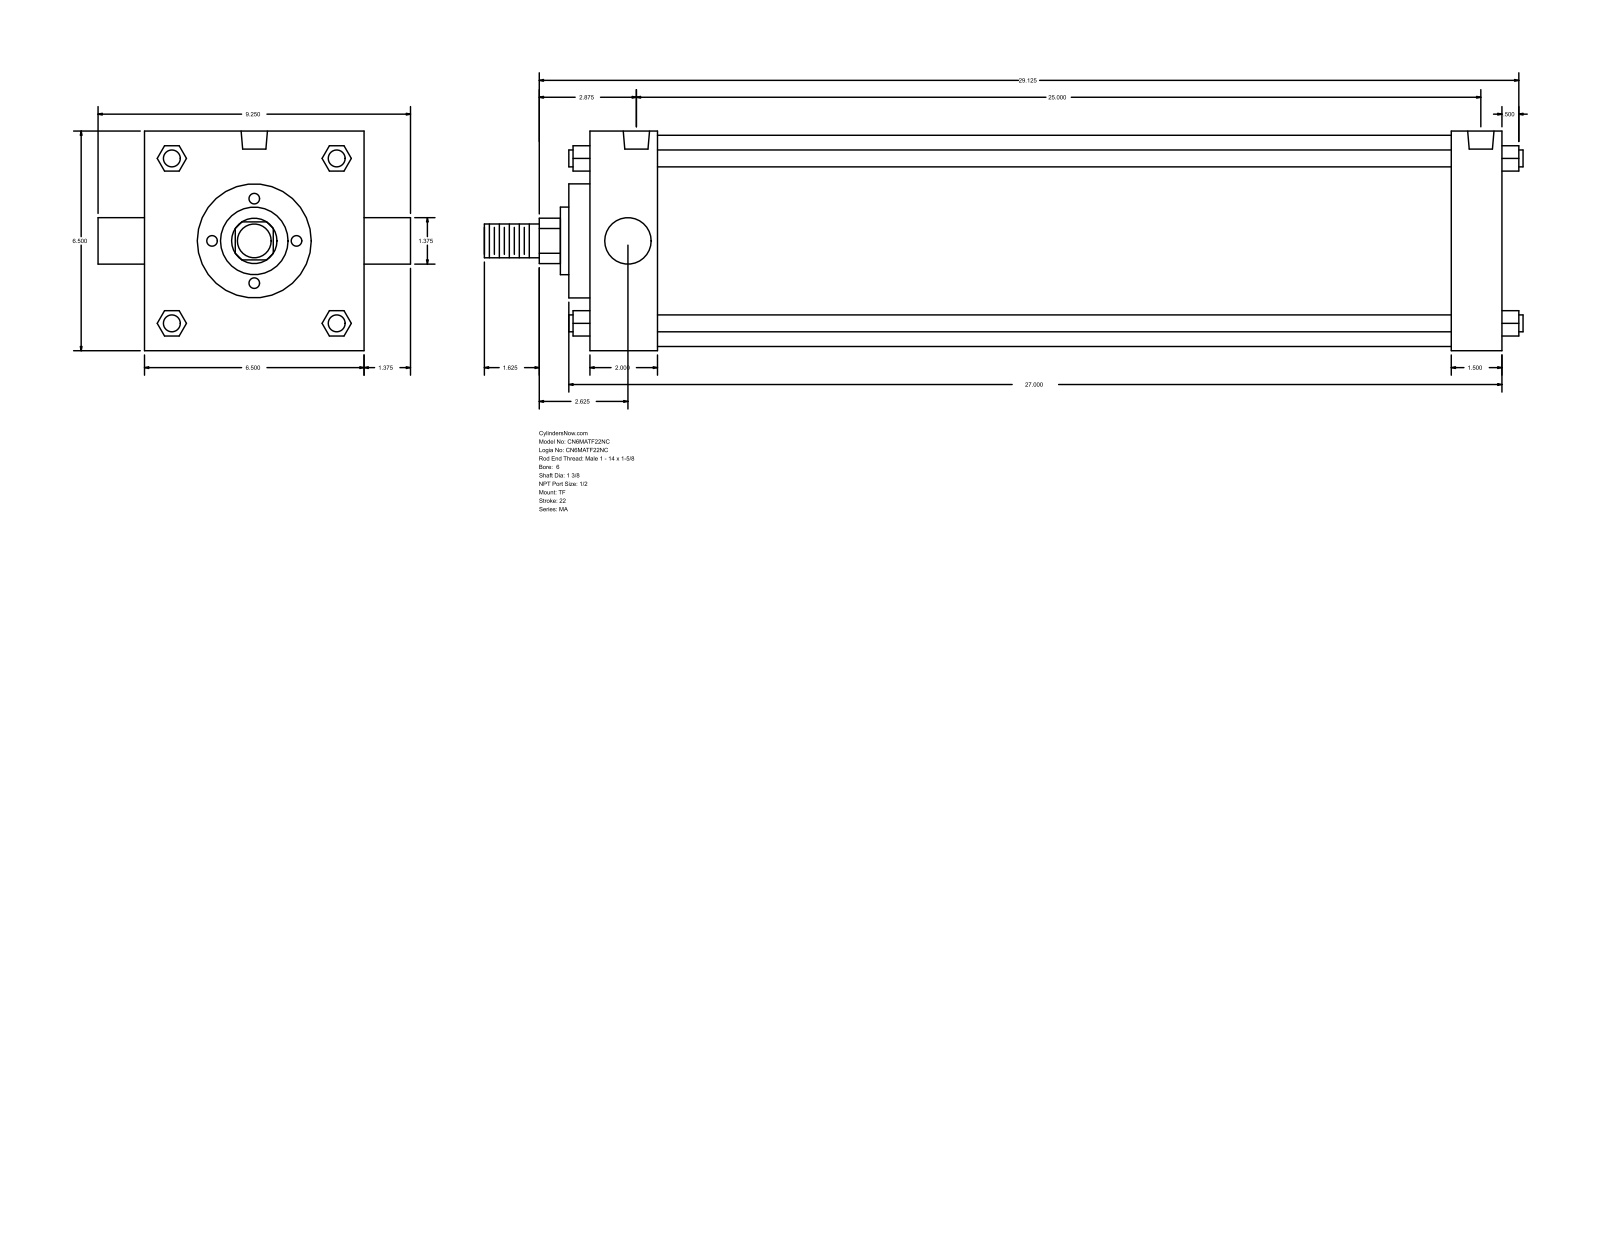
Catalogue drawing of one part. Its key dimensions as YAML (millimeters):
part_name: "MA_TF__0600_1.375"
step_written_by: "GSSL Pune (CONFIG_CONTROL_DESIGN)"
units: millimeters
bodies: {solids: 0, faces: 122, planar: 93, cylindrical: 29, other: 0}
overall_size: [781.05, 234.95, 165.1]
round_holes:
  - {diameter: 17.46, count: 3}
  - {diameter: 19.77, count: 2}
round_bosses_or_shafts:
  - {diameter: 12.7, count: 4}
  - {diameter: 34.92, count: 2}
  - {diameter: 158.75, count: 1}
  - {diameter: 85.72, count: 1}
  - {diameter: 50.8, count: 1}
  - {diameter: 25.4, count: 1}
partial_cylinders:
  - {radius: 17.06, count: 1}
face_to_face_distances: [165.1, 688.98, 38.1, 50.8, 638.18, 650.88, 600.08, 66.67, 15.87, 666.75]
hole_center_spacings: [3.18, 634.99, 638.17]
